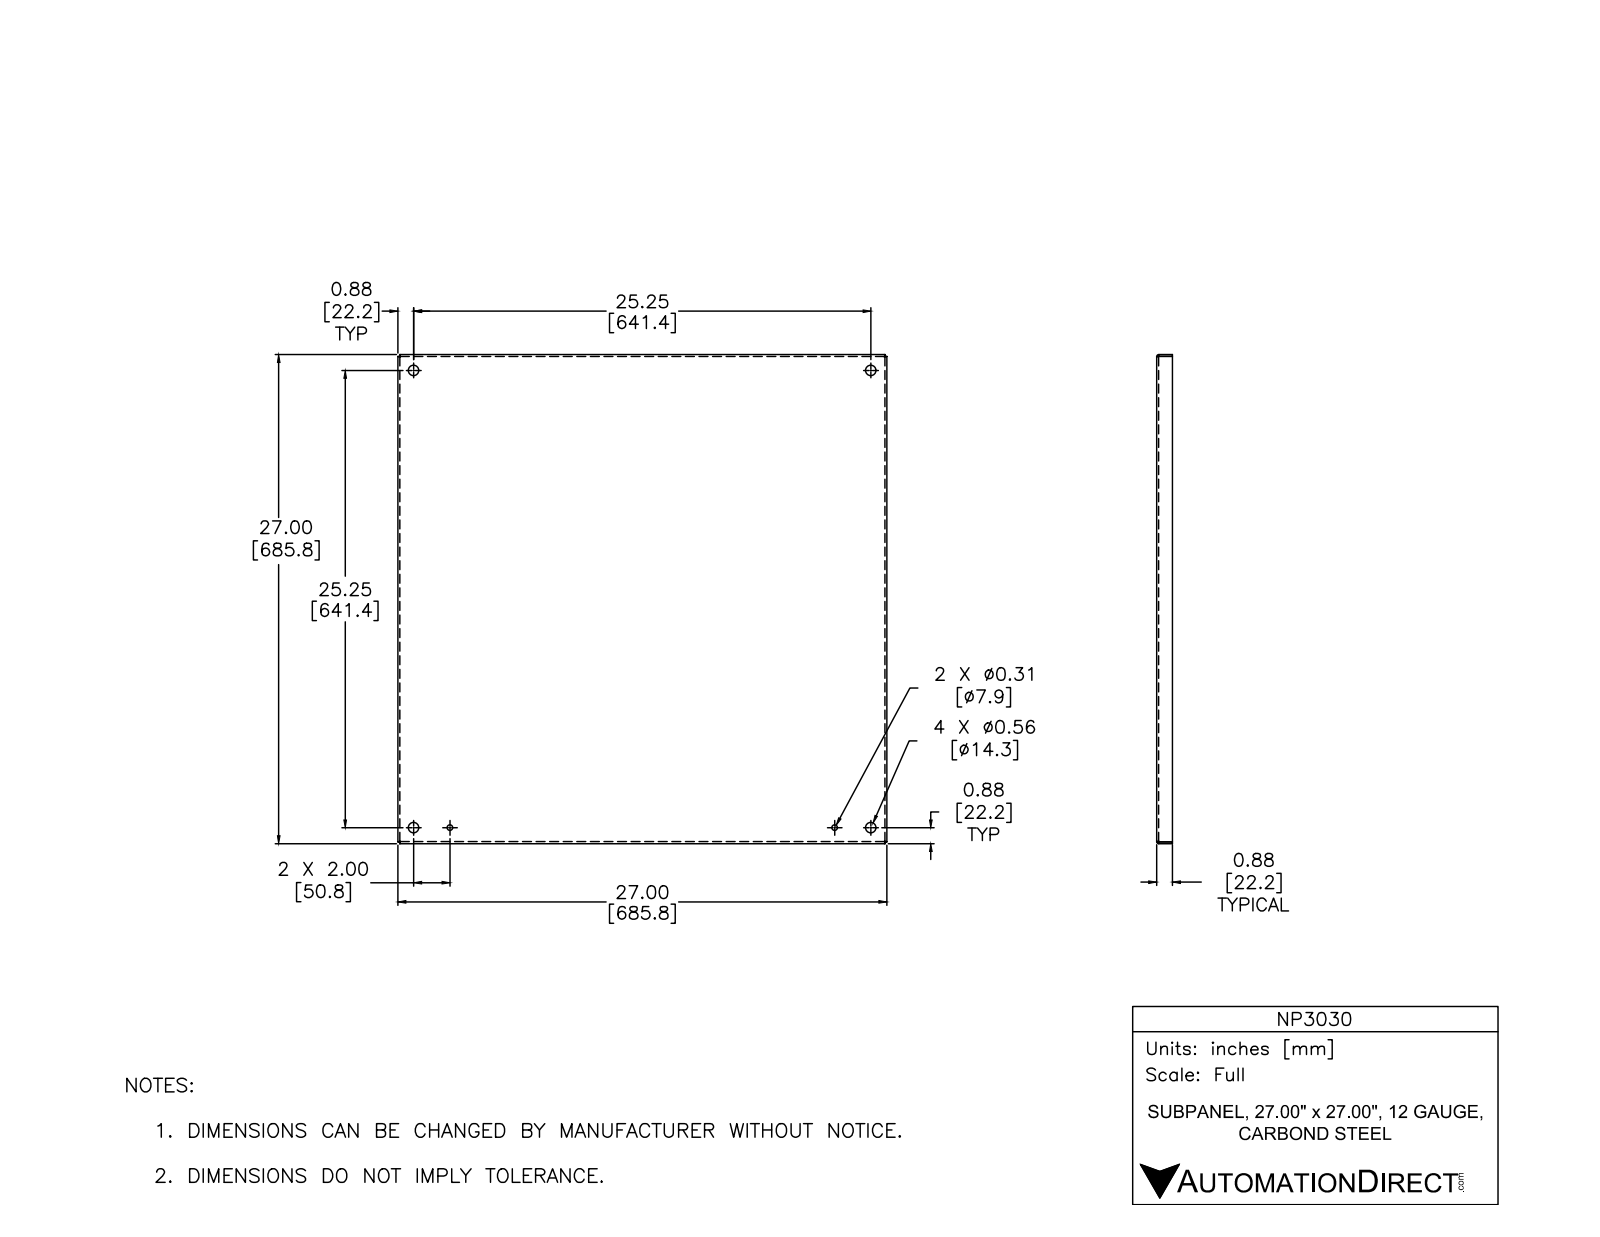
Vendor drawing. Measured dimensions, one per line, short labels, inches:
name: NP3030
written by: Autodesk Inventor 2012 (AUTOMOTIVE_DESIGN)
unit: in
bodies: 1 solid, 44 faces (22 planar, 14 cylindrical, 8 other)
size: 27 × 27 × 0.875
volume: 75.74 in³; area: 1 627 in²
holes: 4× ⌀0.563, 2× ⌀0.312
rounds: 4× R0.031, 4× R0.125
face distances: 0.094, 26.906, 26.813, 27, 0.781, 0.875, 0.105, 26.895, 26.802, 26.791
hole spacings: 25.25, 25.329, 35.709, 2, 2, 21.25, 23.25, 23.25
